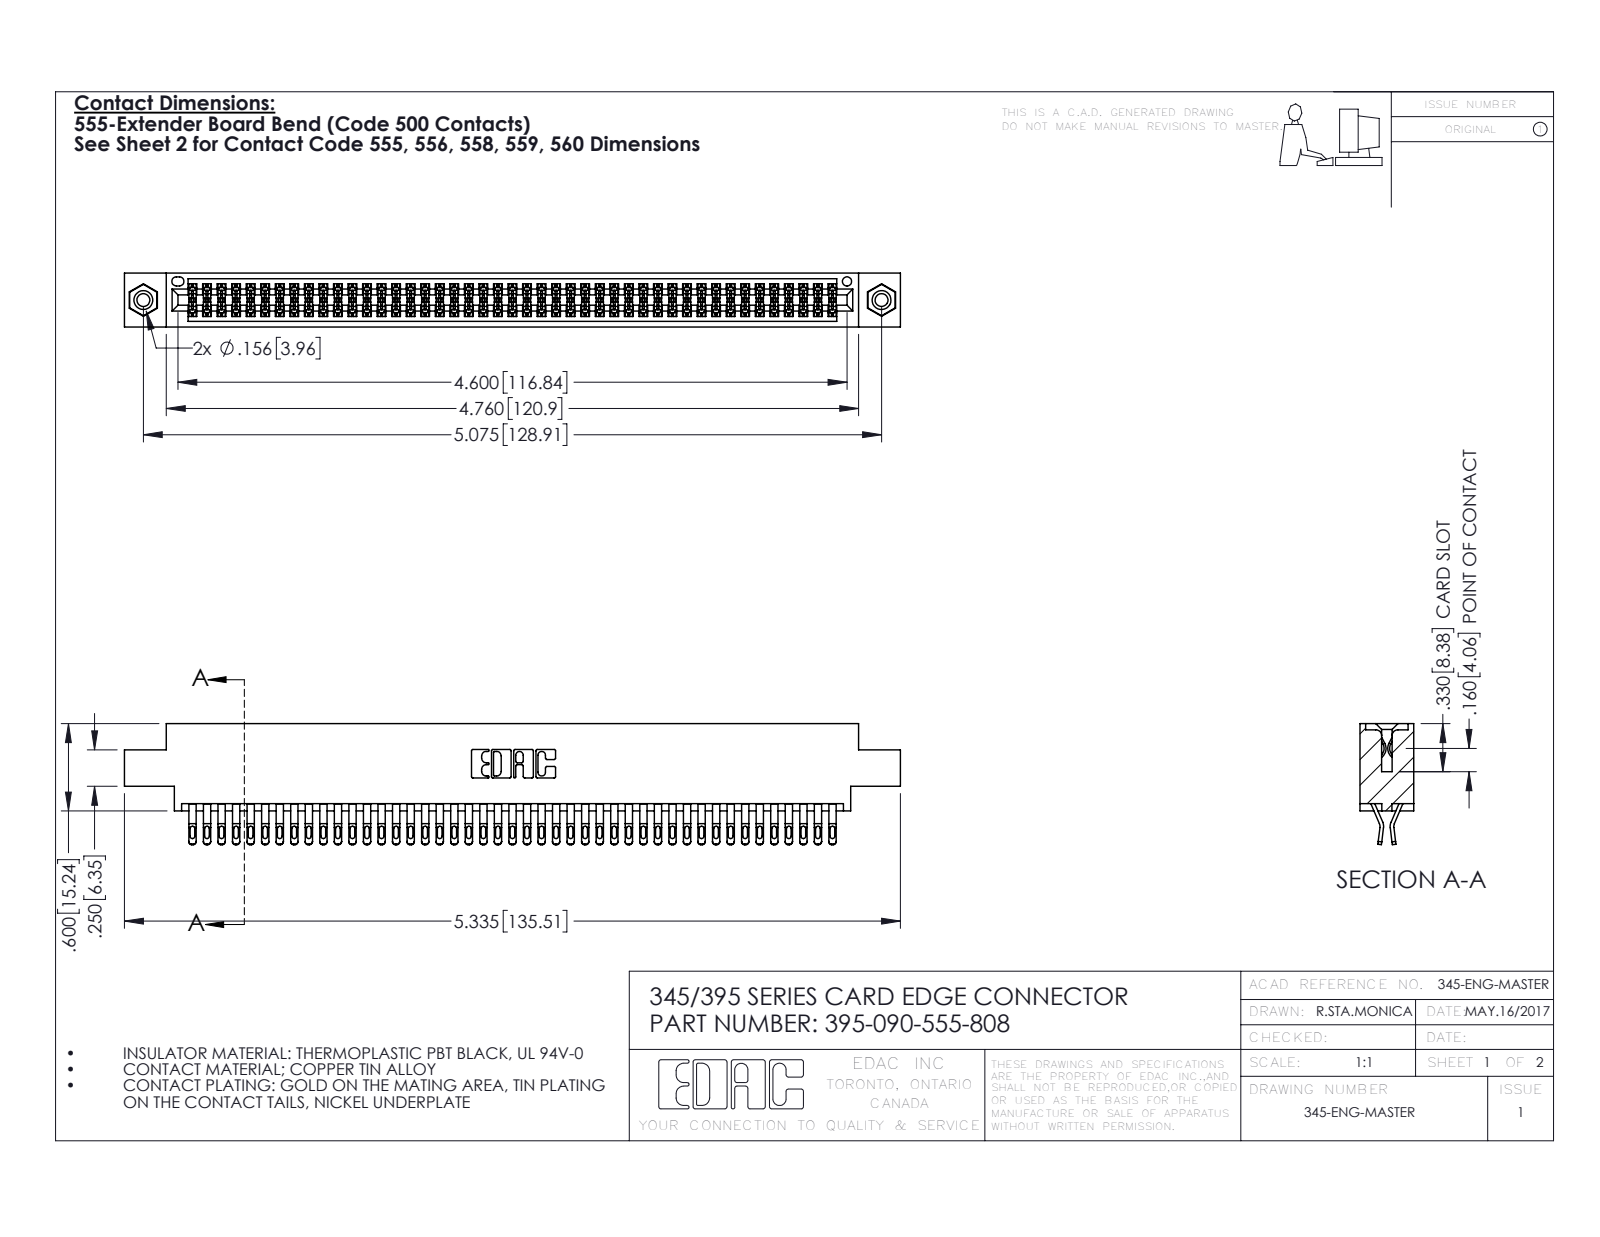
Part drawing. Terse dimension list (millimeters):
name: 345-292-001_555 Tail; 395-090-555-808; 345 Part_0.170 Offset - 0.156 Dia-TI; 345-250-001_345-250-003-102
written by: SolidWorks 2016 (CONFIG_CONTROL_DESIGN)
unit: mm
bodies: 93 solids, 5230 faces (2906 planar, 2308 cylindrical, 16 other)
size: 135.5 × 21.1 × 9.4
volume: 13 300 mm³; area: 20 830 mm²
holes: 2× ⌀2.3, 2× ⌀3.2, 2× ⌀4, 1× ⌀1.6
bosses: 2× ⌀3.9
rounds: 225× R0.4, 180× R0.5, 135× R0.2, 22× R0.3, 6× R0.2, 6× R0.8, 3× R0.7, 2× R0.3
face distances: 1.8, 7.6, 9.4, 0.6, 5.1, 2.5, 6.9, 5.7, 4.4, 3.8
hole spacings: 6.9, 122.9, 128.9
